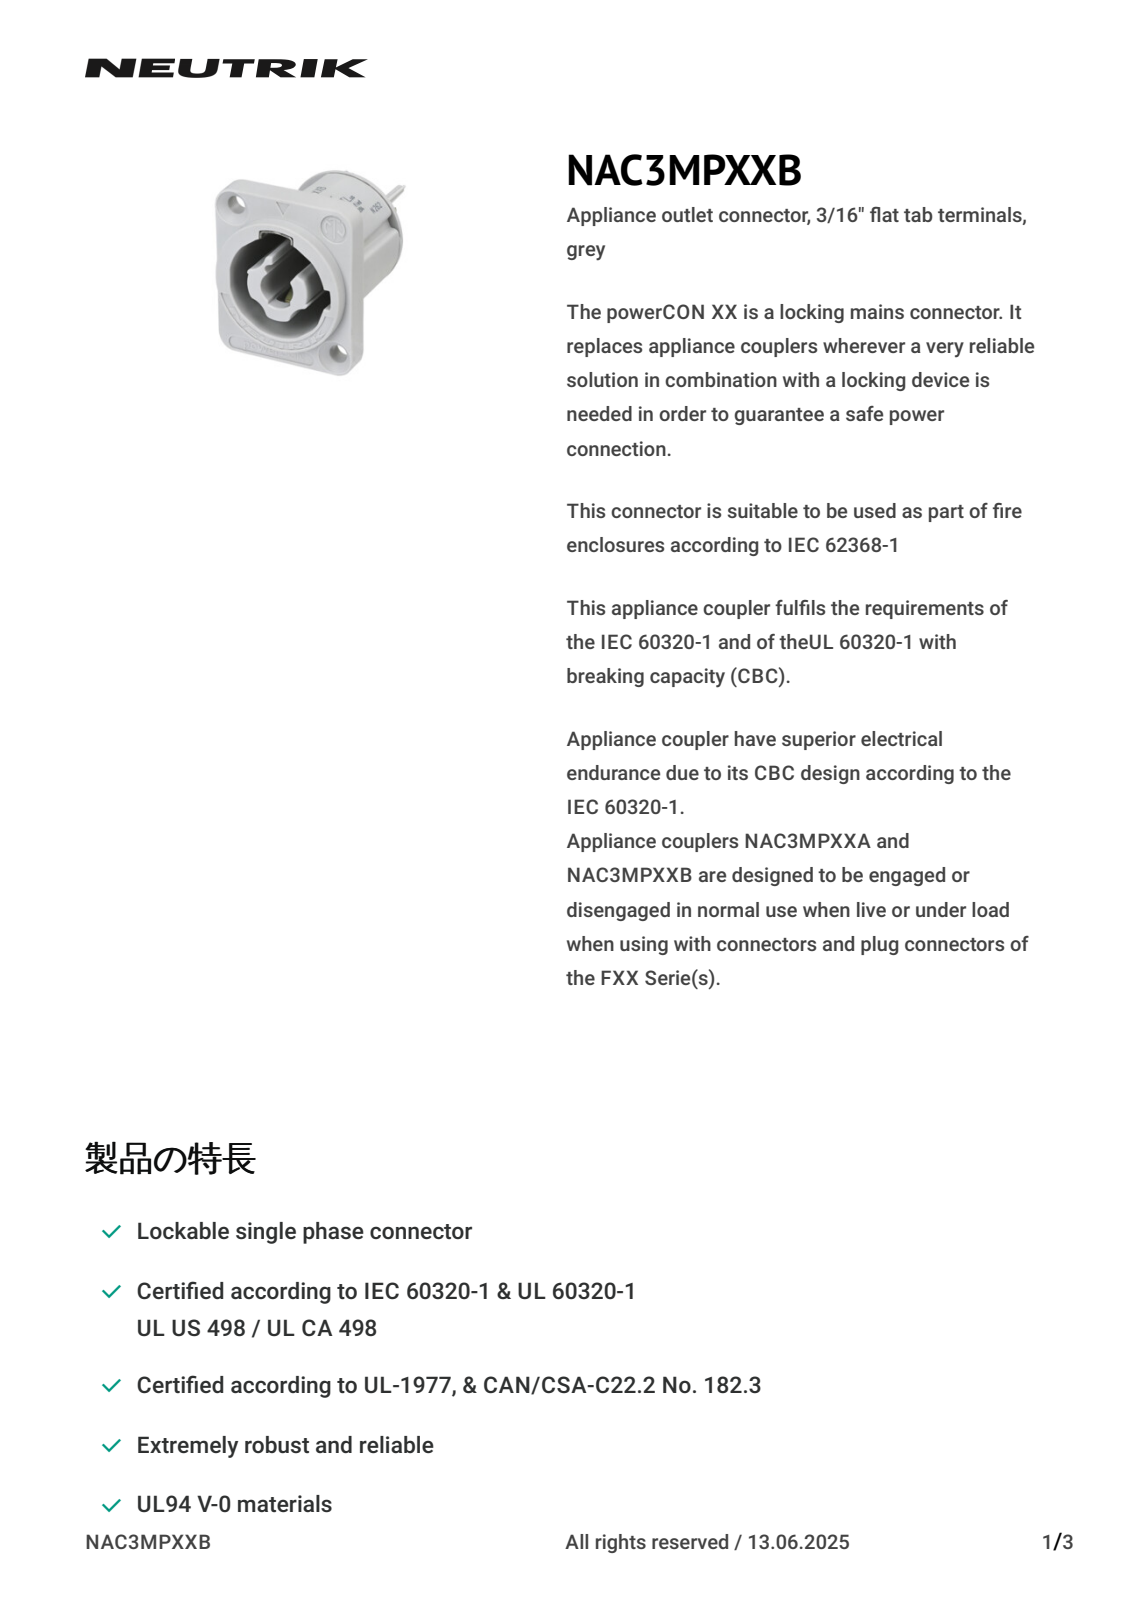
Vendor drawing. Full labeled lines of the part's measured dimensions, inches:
Part name (STEP PRODUCT): NAC3MPXXA
STEP written by: CREO PARAMETRIC BY PTC INC, 2019080 (CONFIG_CONTROL_DESIGN)
Units: inches
Bodies: 1 solid, 1243 faces (384 planar, 194 cylindrical, 665 other)
Overall size (bounding box): 1.461 × 1.217 × 1.02
Volume: 0.66 in³ · Surface area: 9.982 in²
Round holes (diameter × count): ⌀0.055 ×2, ⌀0.236 ×2, ⌀0.165 ×1, ⌀0.197 ×1
Round bosses / shafts (diameter × count): ⌀0.772 ×1, ⌀0.144 ×1
Partial cylindrical surfaces — rounded edges, fillets, slot ends (radius × count): R0.008 ×58, R0.02 ×21, R0.012 ×20, R0.01 ×15, R0.008 ×9, R0.006 ×7, R0.011 ×3, R0.006 ×2
Main face-to-face distances: 0.179, 0.098, 0.278, 0.929, 0.927, 0.177, 0.75, 0.1, 1.028, 0.805
Hole centre spacings: 0.82, 0.431, 0.748, 0.945, 1.205
